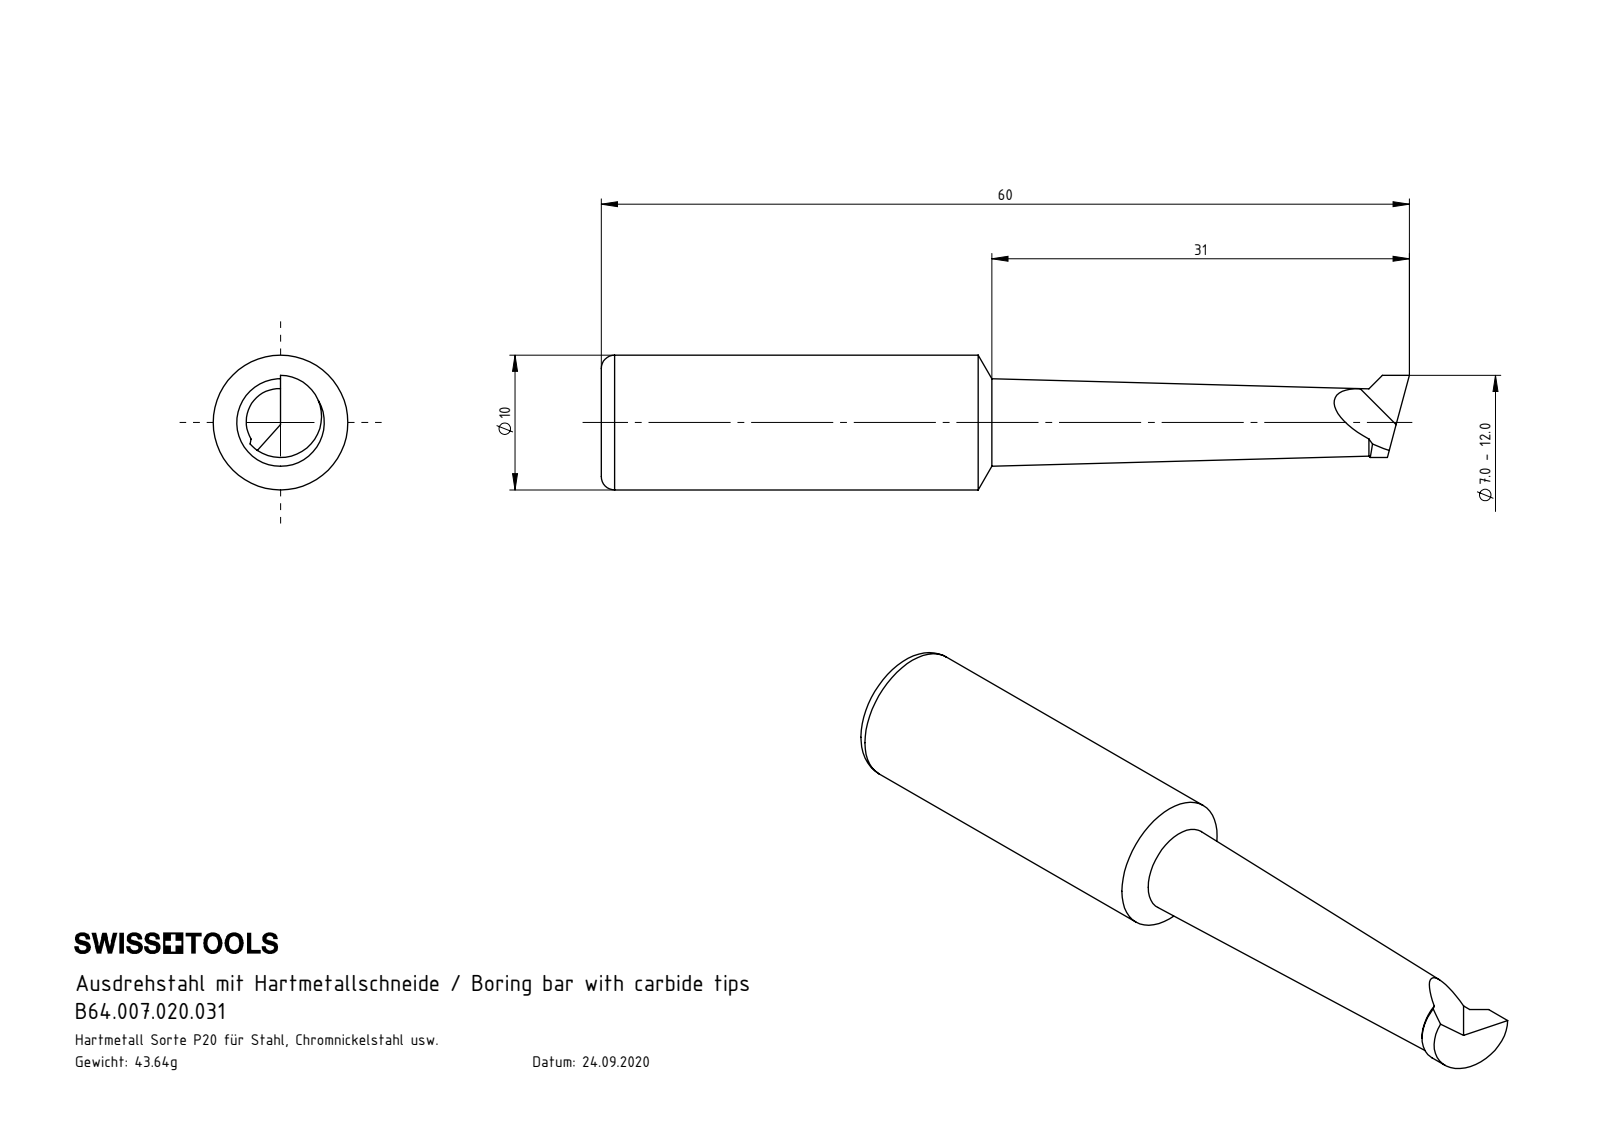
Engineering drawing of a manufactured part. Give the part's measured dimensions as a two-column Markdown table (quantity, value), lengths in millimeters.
| quantity | value |
| --- | --- |
| part name | B64.007.020.031 |
| STEP written by | SolidWorks 2022 (CONFIG_CONTROL_DESIGN) |
| units | millimeters |
| bodies | 1 solid, 14 faces (4 planar, 3 cylindrical, 7 other) |
| overall size | 60 × 10 × 10 |
| volume | 3 010 mm³ |
| surface area | 1 559 mm² |
| round bosses / shafts (diameter × count) | 10 × 1 |
| partial cylindrical surfaces (radius × count) | 3.05 × 1 |
